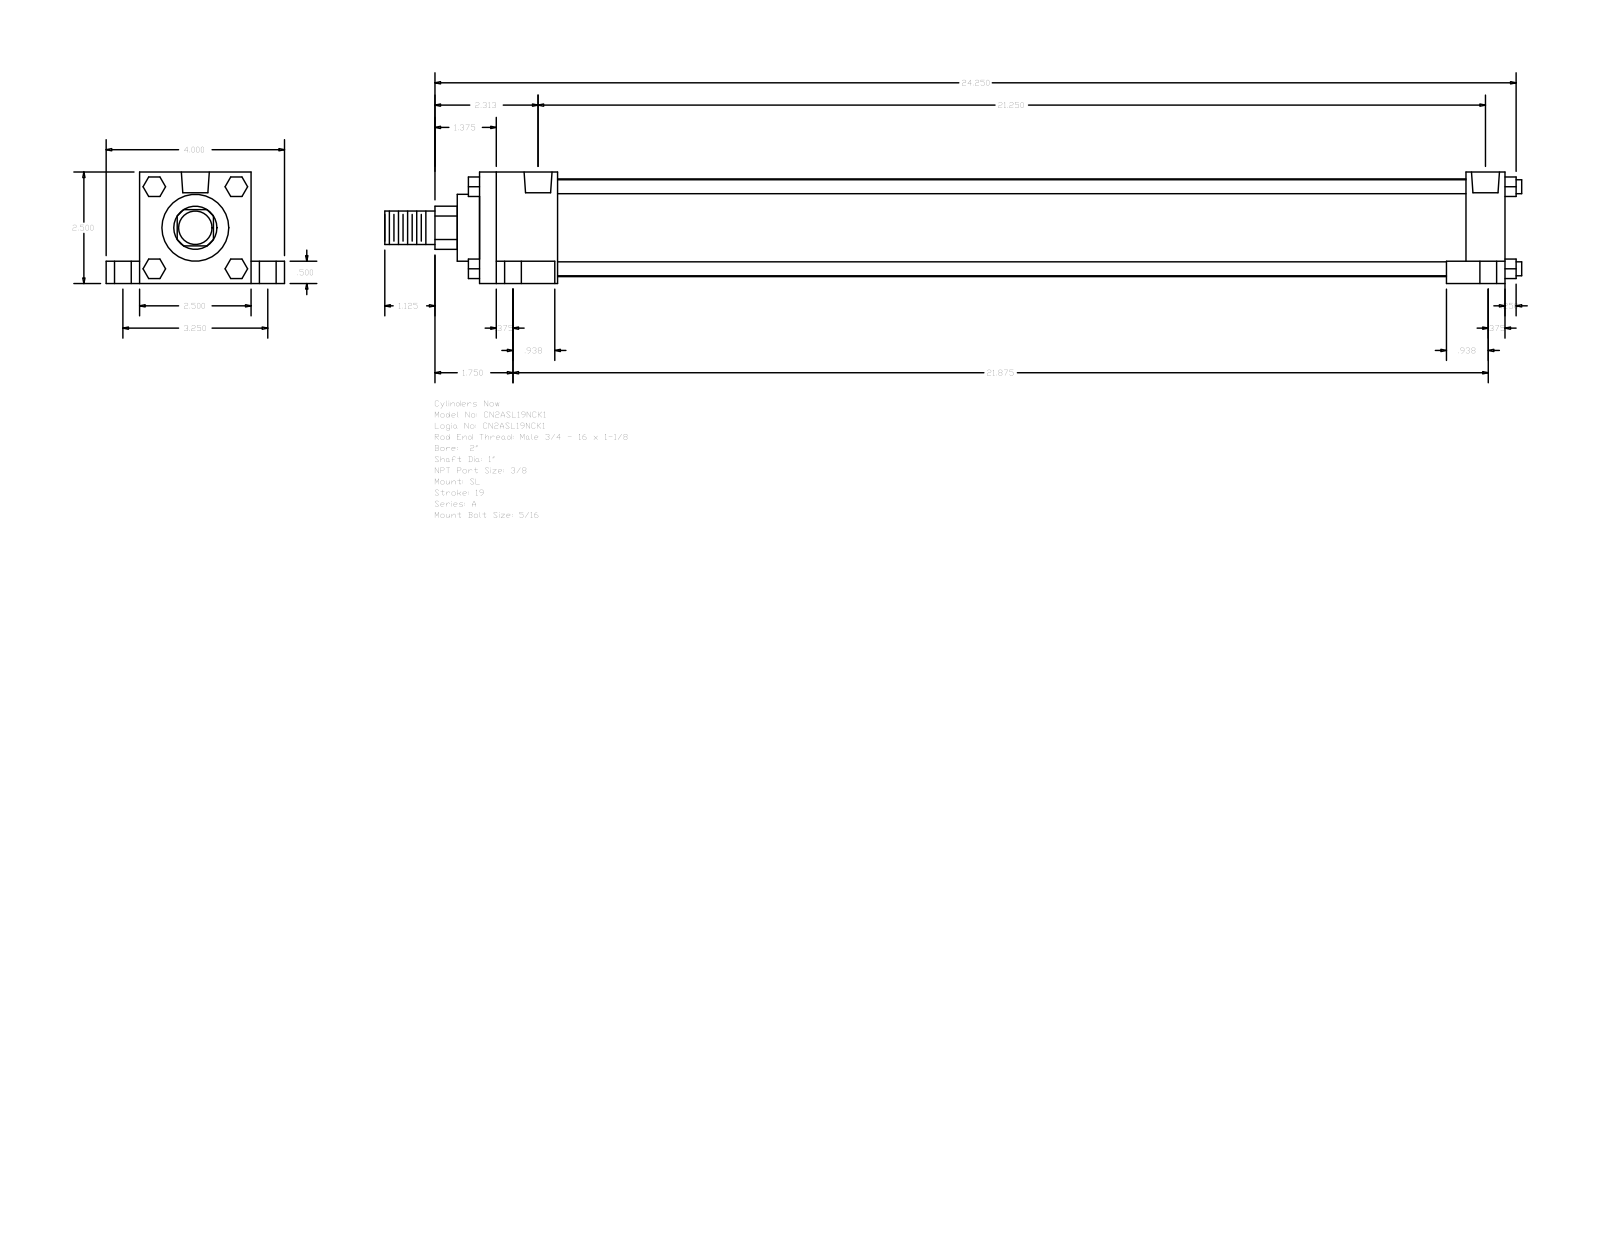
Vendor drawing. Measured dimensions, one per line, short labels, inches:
name: A_SL__0200_1
written by: GSSL Pune (CONFIG_CONTROL_DESIGN)
unit: in
bodies: 0 solids, 148 faces (112 planar, 36 cylindrical, 0 other)
size: 25.5 × 4 × 2.5
holes: 4× ⌀0.219, 4× ⌀0.375, 4× ⌀0.625, 2× ⌀0.627
bosses: 4× ⌀0.313, 1× ⌀2.19, 1× ⌀1.5, 1× ⌀1, 1× ⌀0.75
rounds: 1× R0.484
face distances: 2.5, 23, 0.5, 2, 0.875, 0.75, 3.25, 1.75, 21.25, 22.125
hole spacings: 1.626, 1.639, 1.719, 1.741, 3.25, 21.031, 21.312, 21.374
